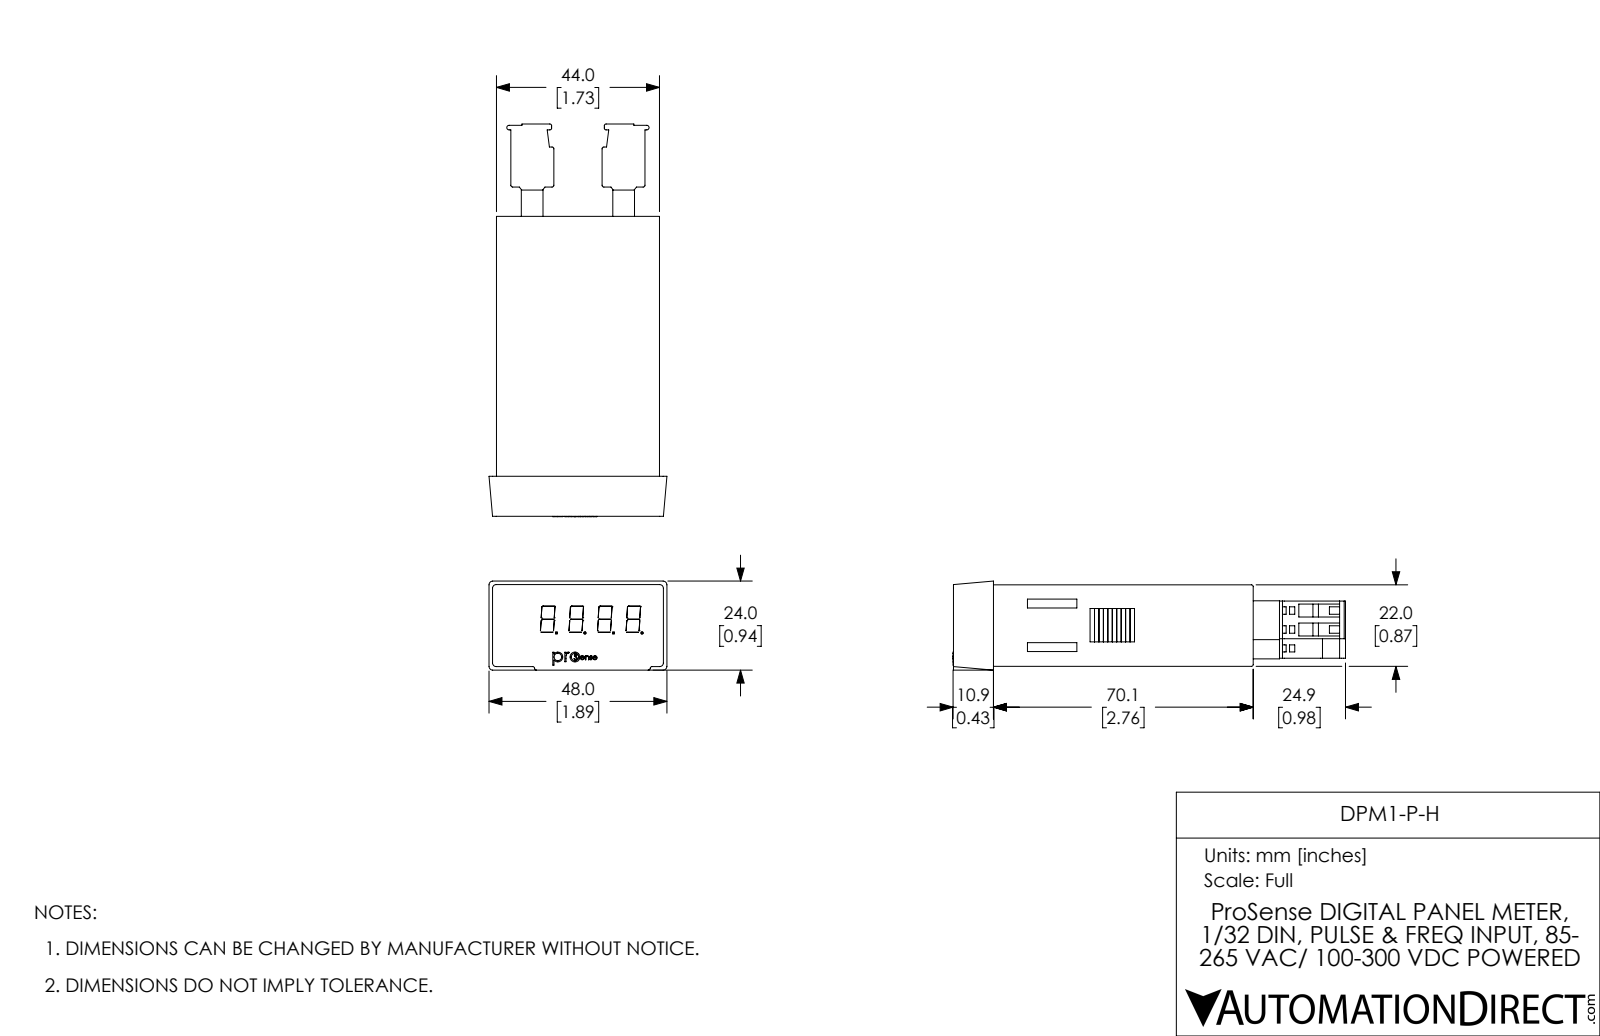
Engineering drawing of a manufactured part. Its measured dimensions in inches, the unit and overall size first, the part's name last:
Units: inches
Overall size (bounding box): 4.169 × 1.89 × 0.945
Round holes (diameter × count): ⌀0.078 ×5, ⌀0.118 ×5, ⌀0.152 ×5
Partial cylindrical surfaces — rounded edges, fillets, slot ends (radius × count): R0.02 ×14, R0.121 ×5, R0.039 ×4, R0.025 ×2
Main face-to-face distances: 0.059, 0.807, 0.866, 0.748, 1.673, 1.732, 1.614, 0.051, 3.134, 0.433
Hole centre spacings: 0.197, 0.201, 0.398, 0.974, 0.983, 0.983, 0.992, 0.996
Volume: 1.873 in³ · Surface area: 42.97 in²
Bodies: 3 solids, 789 faces (616 planar, 79 cylindrical, 94 other)
Part name (STEP PRODUCT): DPM1-P Coord fXT
STEP written by: SolidWorks 2017 (AUTOMOTIVE_DESIGN)
